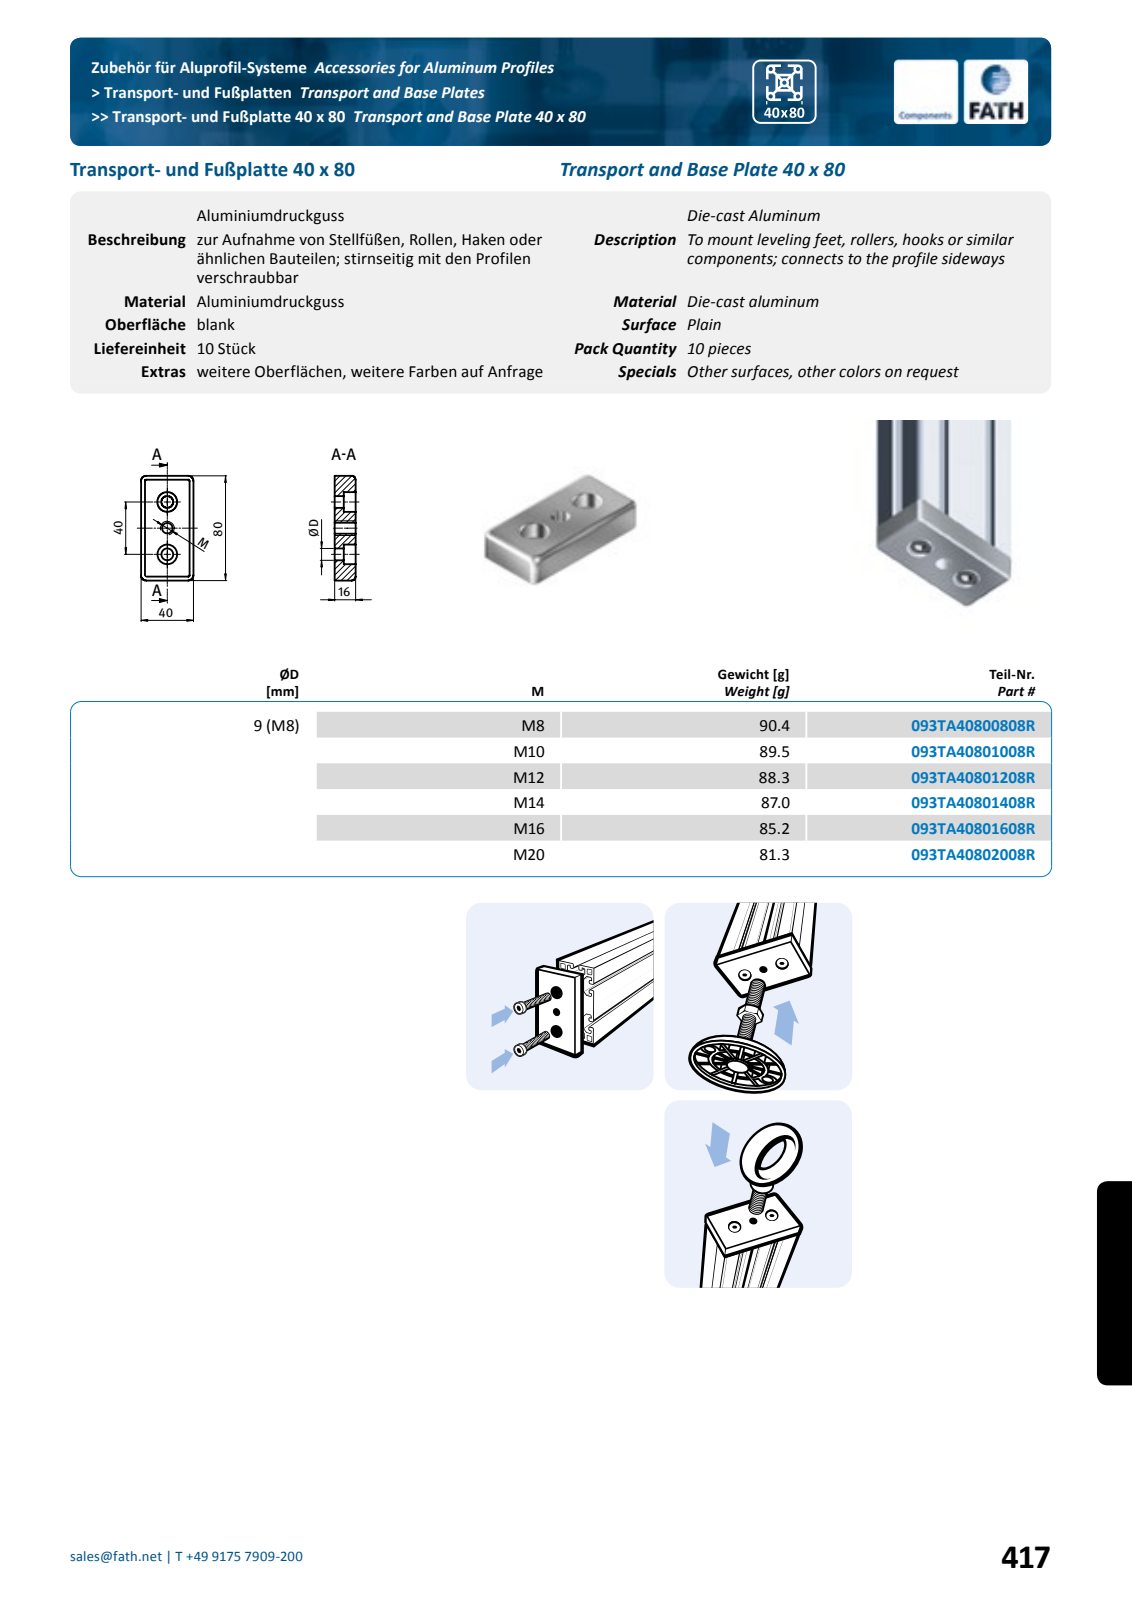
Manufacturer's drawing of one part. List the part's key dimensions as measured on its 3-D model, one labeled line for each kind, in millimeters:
Part name (STEP PRODUCT): fath_093ta40800808r
STEP written by: Spatial InterOp 3D (automotive_design)
Units: millimetres
Bodies: 1 solid, 200 faces (44 planar, 62 cylindrical, 94 other)
Overall size (bounding box): 80 × 40 × 16
Volume: 34 250 mm³ · Surface area: 15 195 mm²
Round holes (diameter × count): ⌀9 ×2, ⌀15 ×2, ⌀6.8 ×1
Partial cylindrical surfaces — rounded edges, fillets, slot ends (radius × count): R1 ×30, R3 ×4, R4 ×4
Main face-to-face distances: 16, 40, 13, 3, 18.98, 80, 58.94, 7, 6, 9
Hole centre spacings: 20, 40
